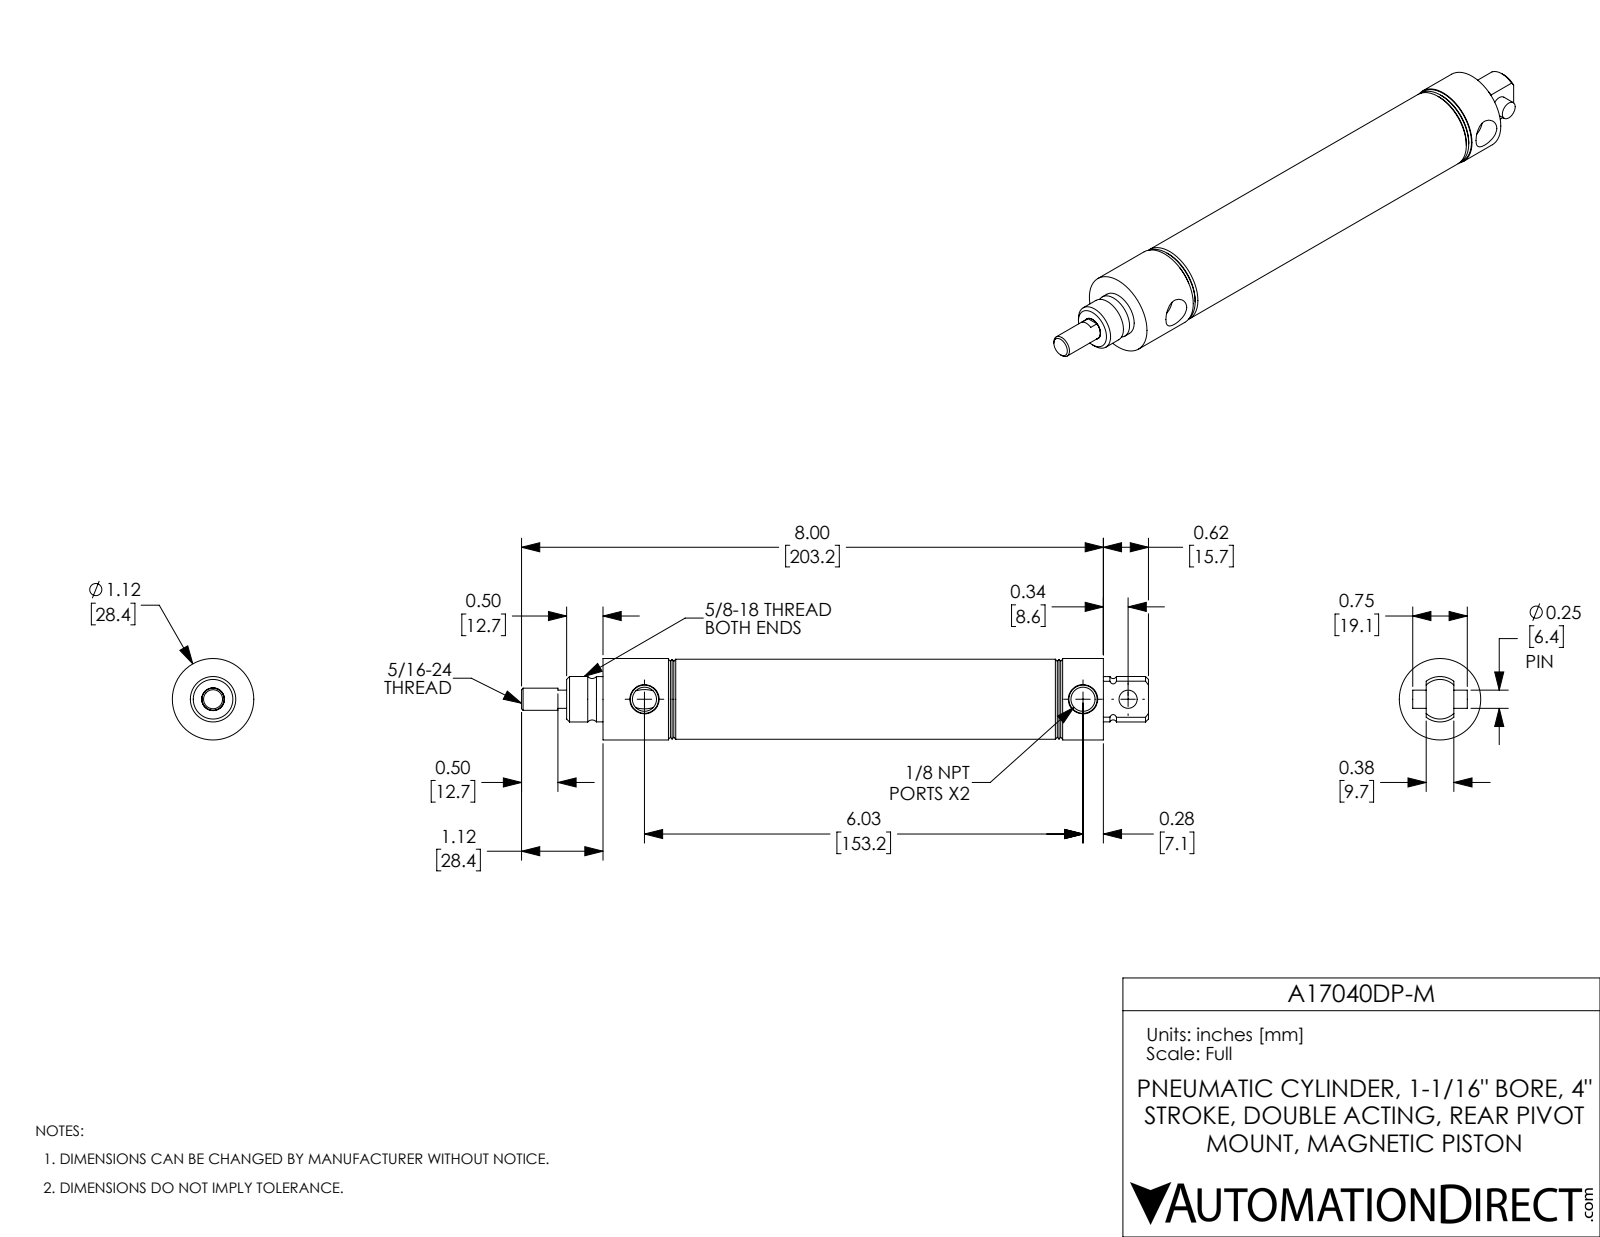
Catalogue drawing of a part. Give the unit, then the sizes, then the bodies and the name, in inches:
Units: inches
Overall size (bounding box): 8.62 × 1.12 × 1.12
Round holes (diameter × count): ⌀0.332 ×2, ⌀0.25 ×1, ⌀0.312 ×1, ⌀1.063 ×1
Round bosses / shafts (diameter × count): ⌀1.12 ×1, ⌀1.1 ×1, ⌀0.625 ×1, ⌀0.623 ×1, ⌀0.304 ×1
Partial cylindrical surfaces — rounded edges, fillets, slot ends (radius × count): R0.313 ×1
Main face-to-face distances: 0.5, 5.69, 4.5, 4, 1.19, 1.69, 5.69, 6.88, 5.19, 1.19
Hole centre spacings: 0.62, 6.03, 6.65
Volume: 3.586 in³ · Surface area: 57.85 in²
Bodies: 3 solids, 92 faces (22 planar, 32 cylindrical, 38 other)
Part name (STEP PRODUCT): A17040DP-M-MainBody; A17040DP-M-Rod; A17040DP-M-PIN; A17040DP-M
STEP written by: SolidWorks 2017 (AUTOMOTIVE_DESIGN)
